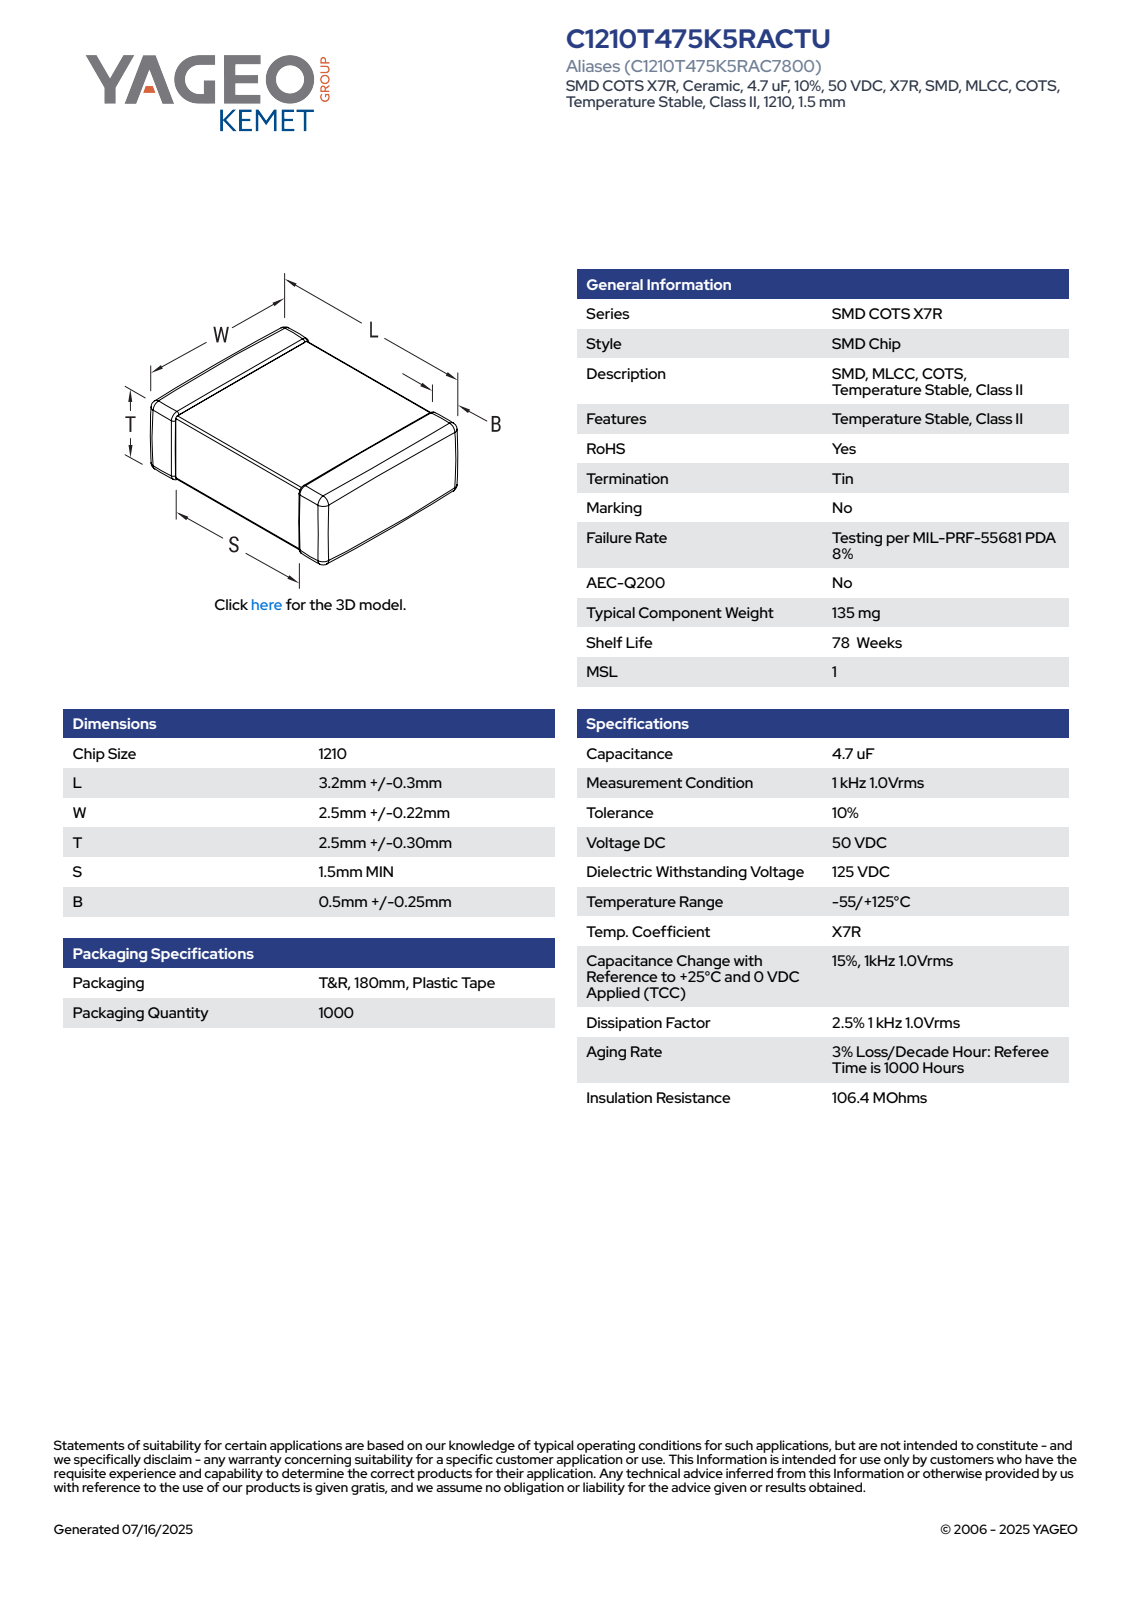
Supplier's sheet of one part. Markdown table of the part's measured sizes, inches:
| quantity | value |
| --- | --- |
| part name | CCSM_STD_1210_L3.5W2.72T2.8S2.5B0.75 |
| STEP written by | SolidWorks 2021 (AUTOMOTIVE_DESIGN) |
| units | inches |
| bodies | 4 solids, 125 faces (71 planar, 38 cylindrical, 16 other) |
| overall size | 0.138 × 0.11 × 0.107 |
| volume | 0.002 in³ |
| surface area | 0.084 in² |
| main face-to-face distances | 0.138, 0.105, 0.108, 0.102, 0.106, 0.107, 0.11, 0.108, 0.106, 0.059 |
